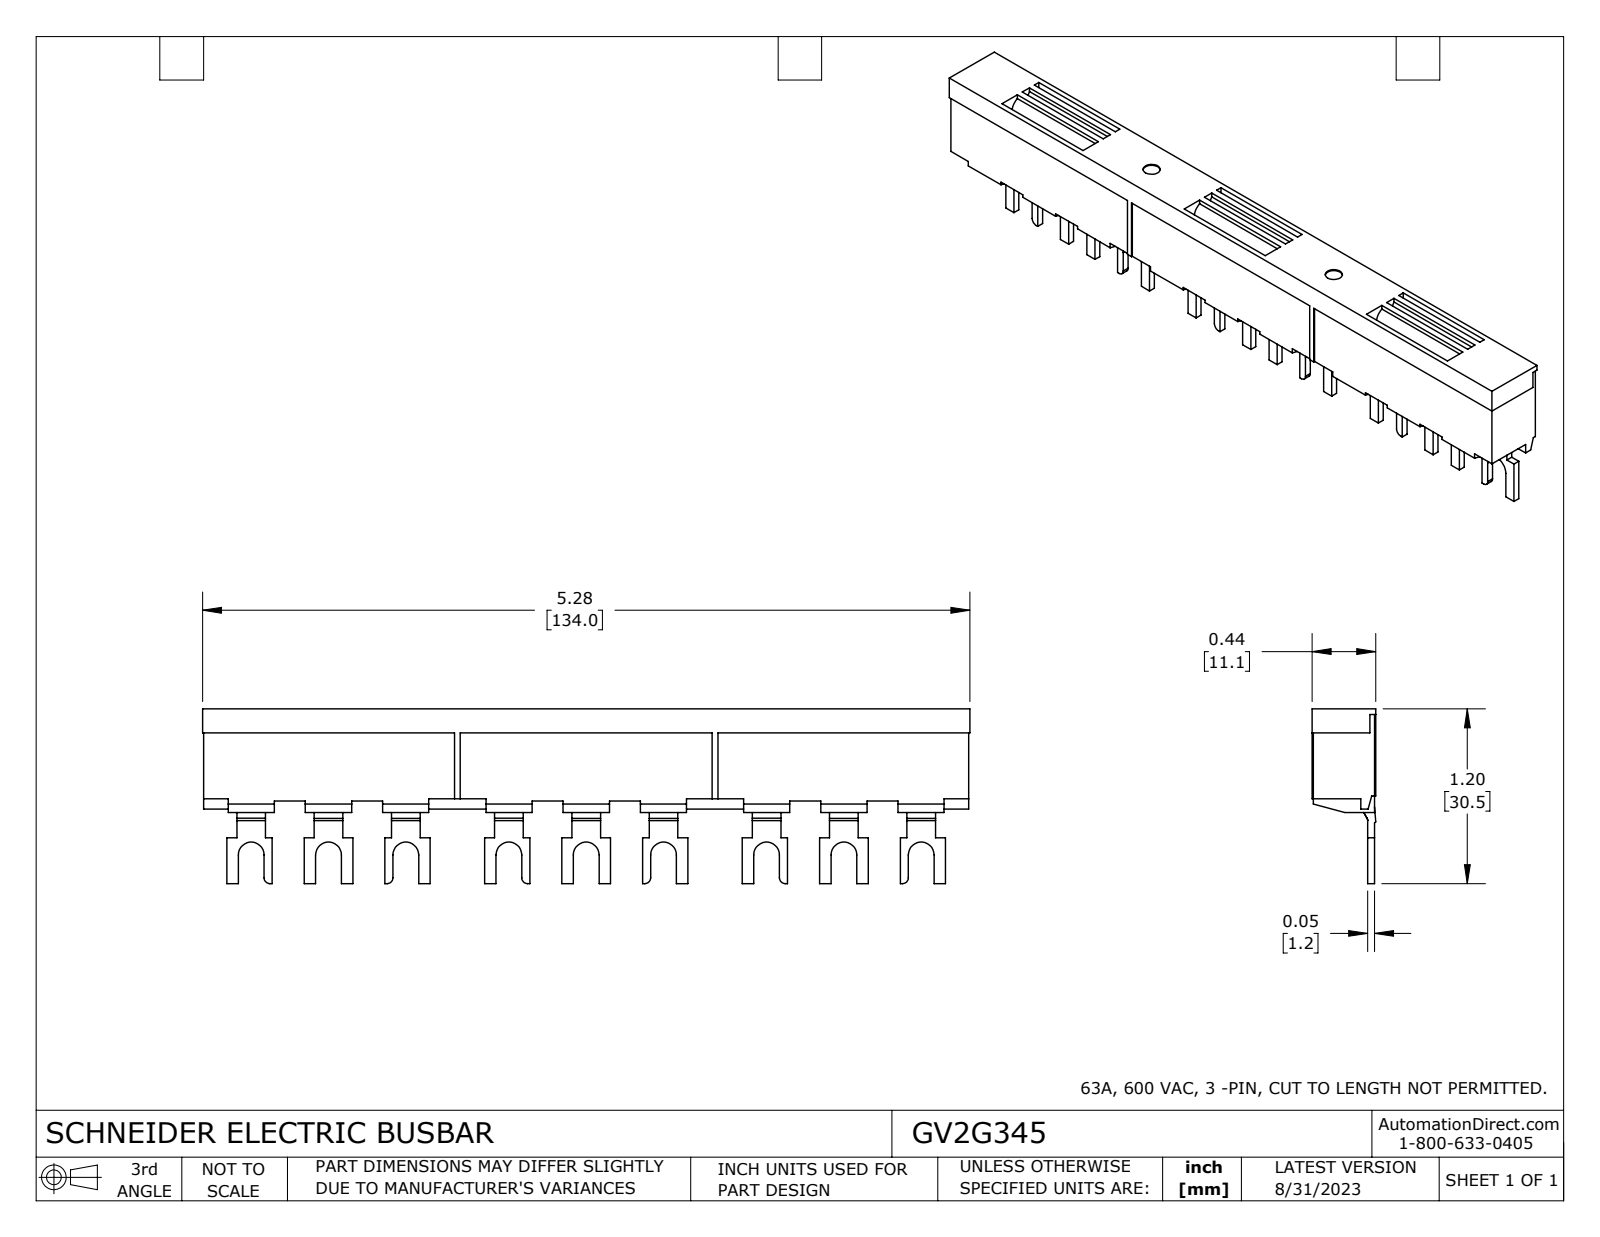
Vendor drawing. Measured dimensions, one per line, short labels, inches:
name: GV2G345
written by: SolidWorks 2021 (CONFIG_CONTROL_DESIGN)
unit: in
bodies: 1 solid, 331 faces (300 planar, 31 cylindrical, 0 other)
size: 5.276 × 1.201 × 0.437
volume: 1.478 in³; area: 16.56 in²
holes: 2× ⌀0.118
rounds: 9× R0.089, 6× R0.039, 1× R0.031, 1× R0.098
face distances: 0.421, 0.429, 0.047, 0.374, 0.382, 0.031, 0.039, 0.634, 0.079, 0.39
hole spacings: 1.772
